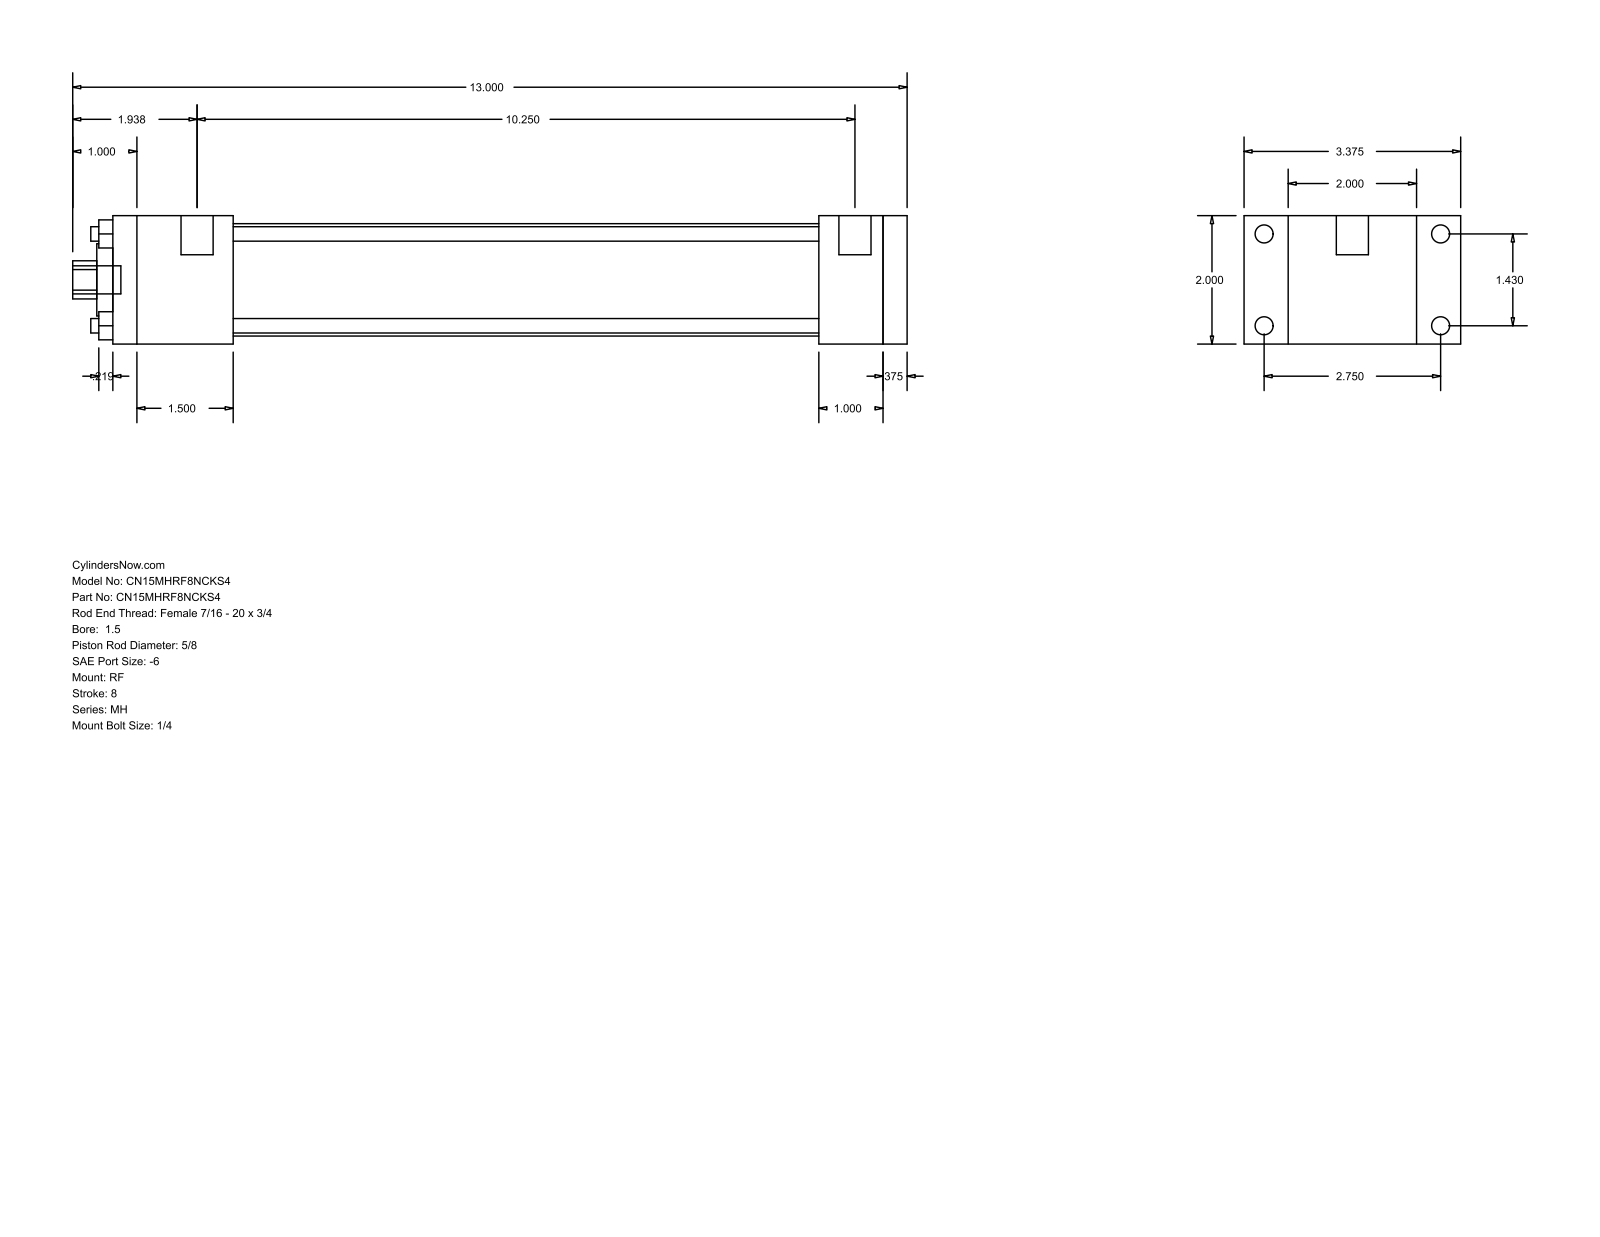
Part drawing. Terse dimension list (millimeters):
name: MH_RF__0150_0.625
written by: GSSL Pune (CONFIG_CONTROL_DESIGN)
unit: mm
bodies: 0 solids, 92 faces (64 planar, 28 cylindrical, 0 other)
size: 330.2 × 85.72 × 50.8
holes: 4× ⌀5.71, 1× ⌀15.88, 1× ⌀28.57, 1× ⌀44.45
bosses: 4× ⌀7.14, 4× ⌀5.56, 2× ⌀12.7, 1× ⌀11.11
rounds: 1× R7.54
face distances: 50.8, 9.52, 304.8, 314.32, 17.46, 68.26, 279.39, 25.41, 34.93, 47.62
hole spacings: 25.68, 36.32, 51.36
